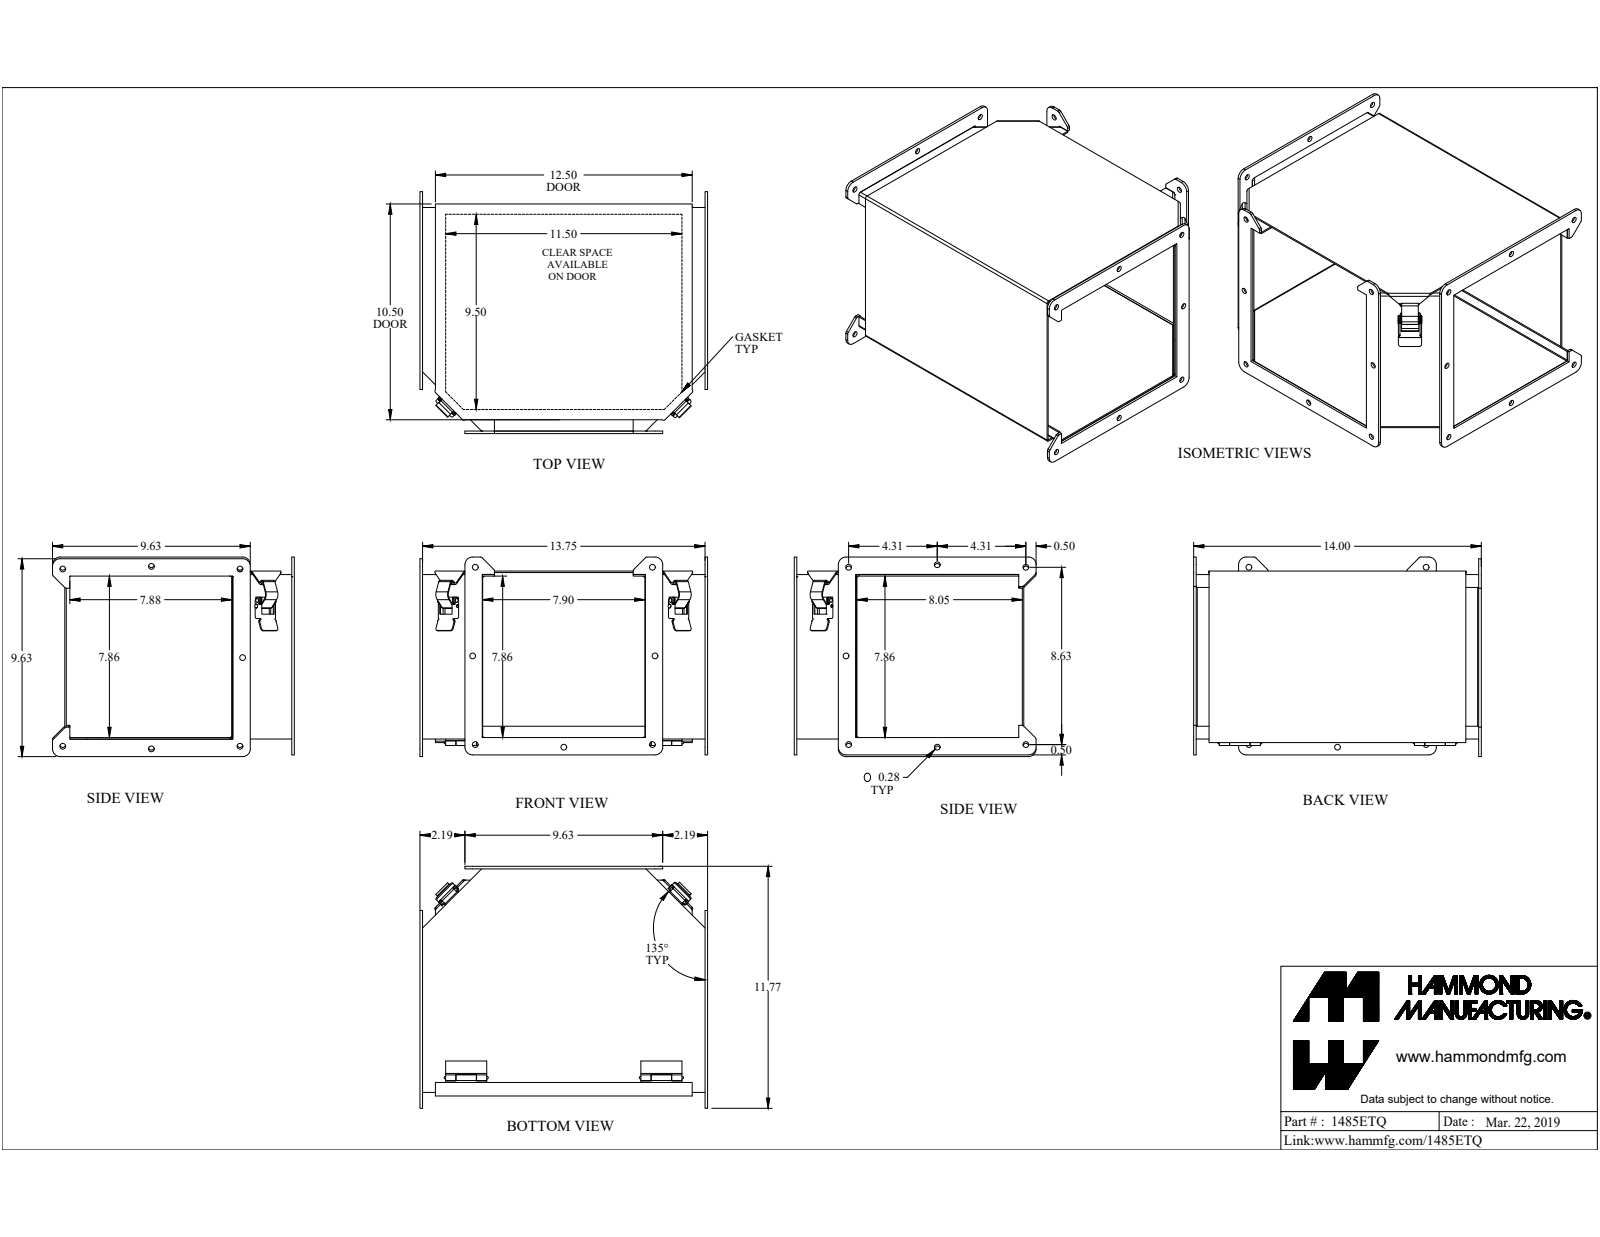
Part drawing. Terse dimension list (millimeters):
name: 1485ETQ
written by: SolidWorks 2019 (CONFIG_CONTROL_DESIGN)
unit: mm
bodies: 17 solids, 505 faces (288 planar, 189 cylindrical, 28 other)
size: 355.6 × 299 × 246.6
volume: 772 200 mm³; area: 808 400 mm²
holes: 21× ⌀7.1, 4× ⌀4.2, 2× ⌀3.3, 1× ⌀3.2
bosses: 6× ⌀4.7, 4× ⌀4, 2× ⌀3.2, 1× ⌀7, 1× ⌀7, 1× ⌀3.2
rounds: 20× R3.2, 14× R0.4, 12× R0.9, 12× R2.7, 12× R9.5, 8× R0.9, 6× R1, 6× R1.9
face distances: 1.8, 205.7, 4.4, 207.6, 203.9, 201.4, 6.2, 2.5, 199.5, 203.2
hole spacings: 109.6, 247.8, 219.1, 219.1, 109.6, 247.8, 159.4, 2.1
